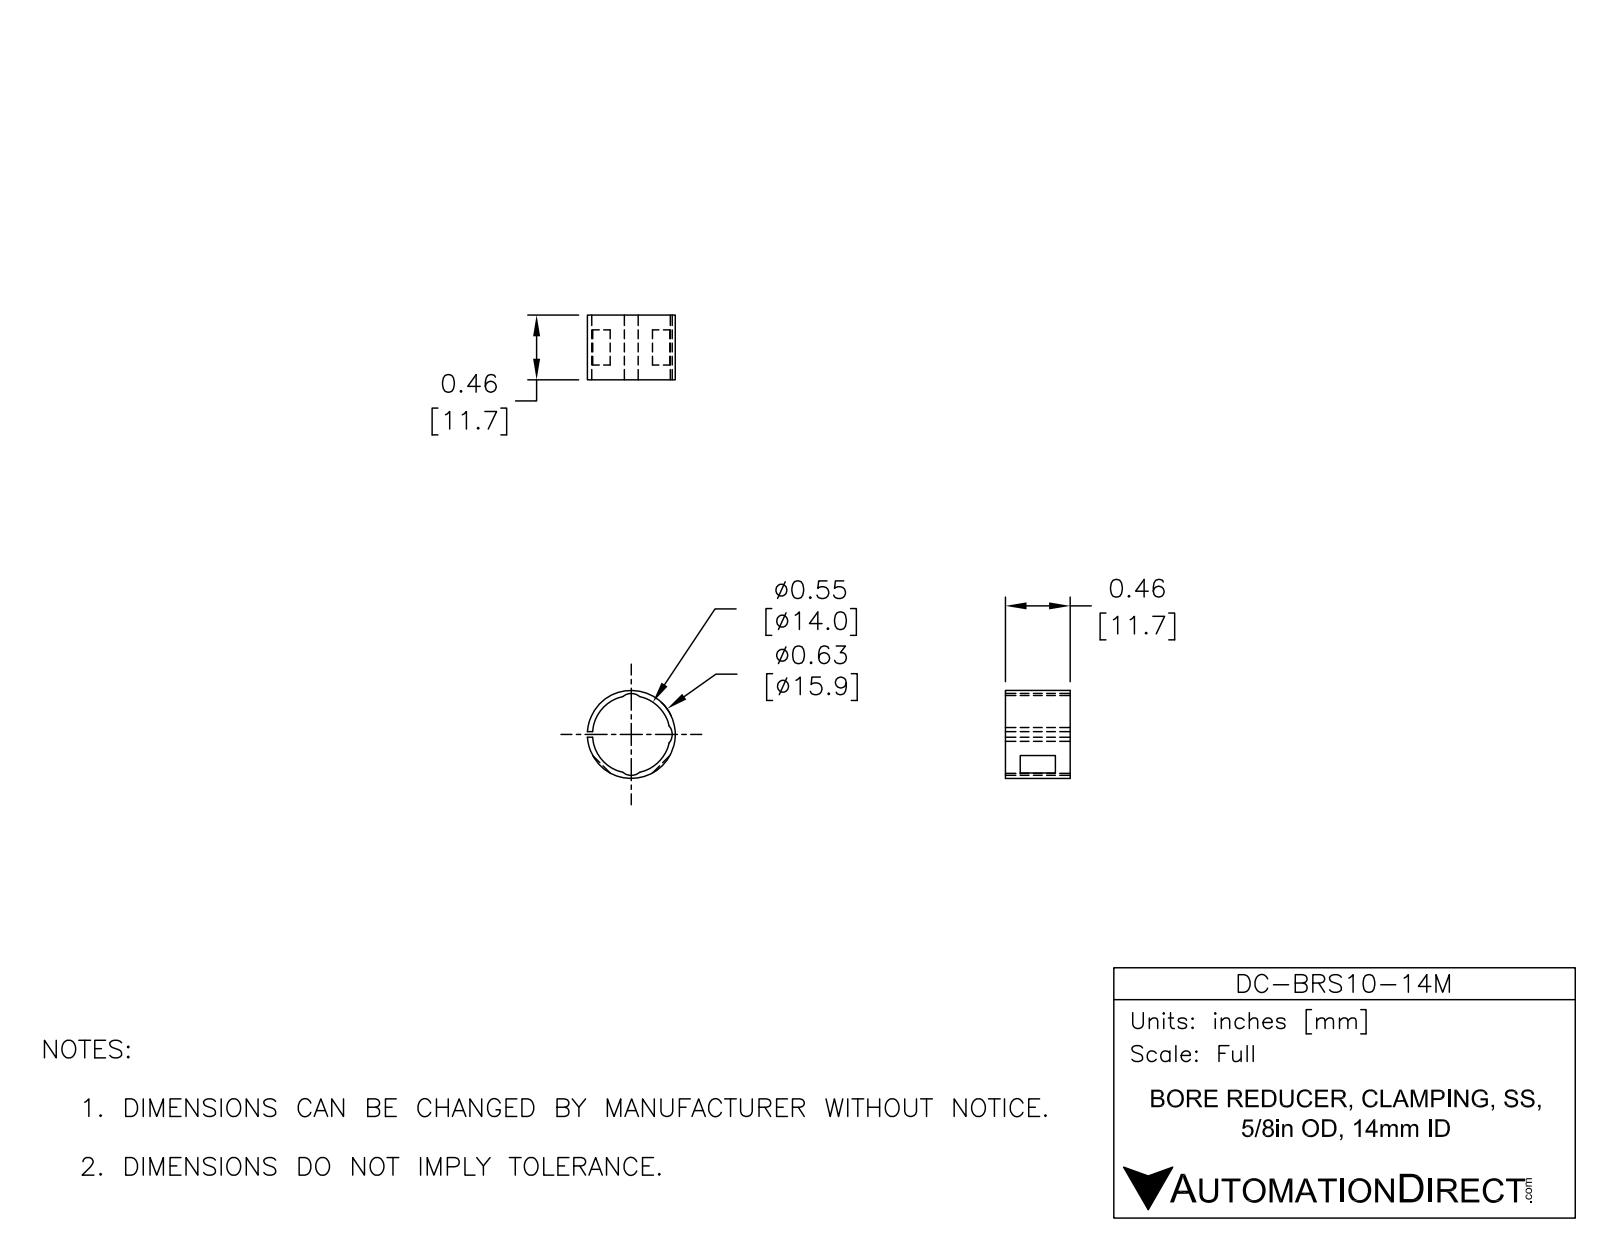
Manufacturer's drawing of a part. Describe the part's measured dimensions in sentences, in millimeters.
The part is named "DC-BRS10-14M". Its 3-D file was written by "SolidWorks 2015 (AUTOMOTIVE_DESIGN)". It is 1 solid with 21 faces: 10 planar, 11 cylindrical and 0 other. Overall it measures 15.88 by 15.86 by 11.68 millimeters. Its volume is 462 cubic millimeters and its surface area 1 187 square millimeters. Round bosses or shafts: 1 of diameter 15.88. Partial cylindrical surfaces (rounded edges, fillets, slot ends): 3 of radius 2.38, 1 of radius 7. The main face-to-face distances are 11.68, 1.02, 2.67, 9.01, 6.34.
